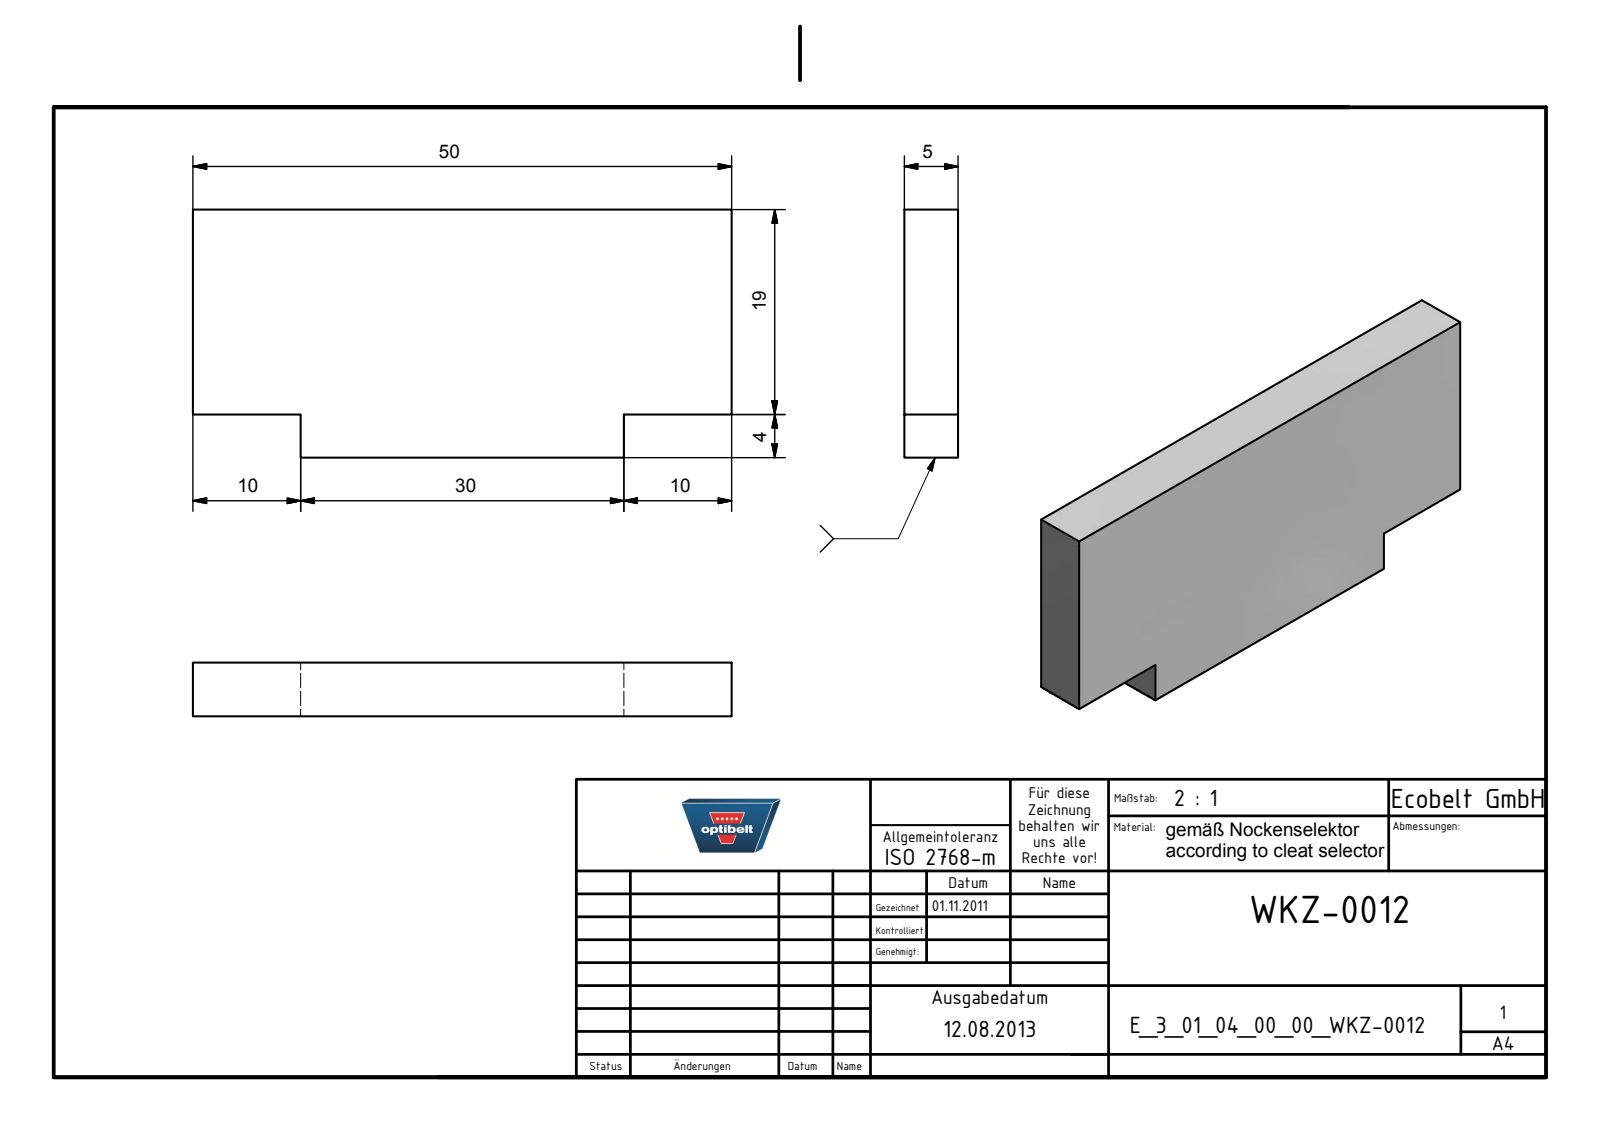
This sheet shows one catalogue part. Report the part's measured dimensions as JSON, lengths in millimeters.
{"part_name": "E_3_01_04_00_00_WKZ-0012", "step_written_by": "Autodesk Inventor 2021 (AUTOMOTIVE_DESIGN)", "units": "millimeters", "bodies": {"solids": 1, "faces": 10, "planar": 10, "cylindrical": 0, "other": 0}, "overall_size": [50, 23, 5], "volume_mm3": 5350, "surface_area_mm2": 2870, "face_to_face_distances": [5, 23, 4, 19, 50, 10, 40, 30]}
